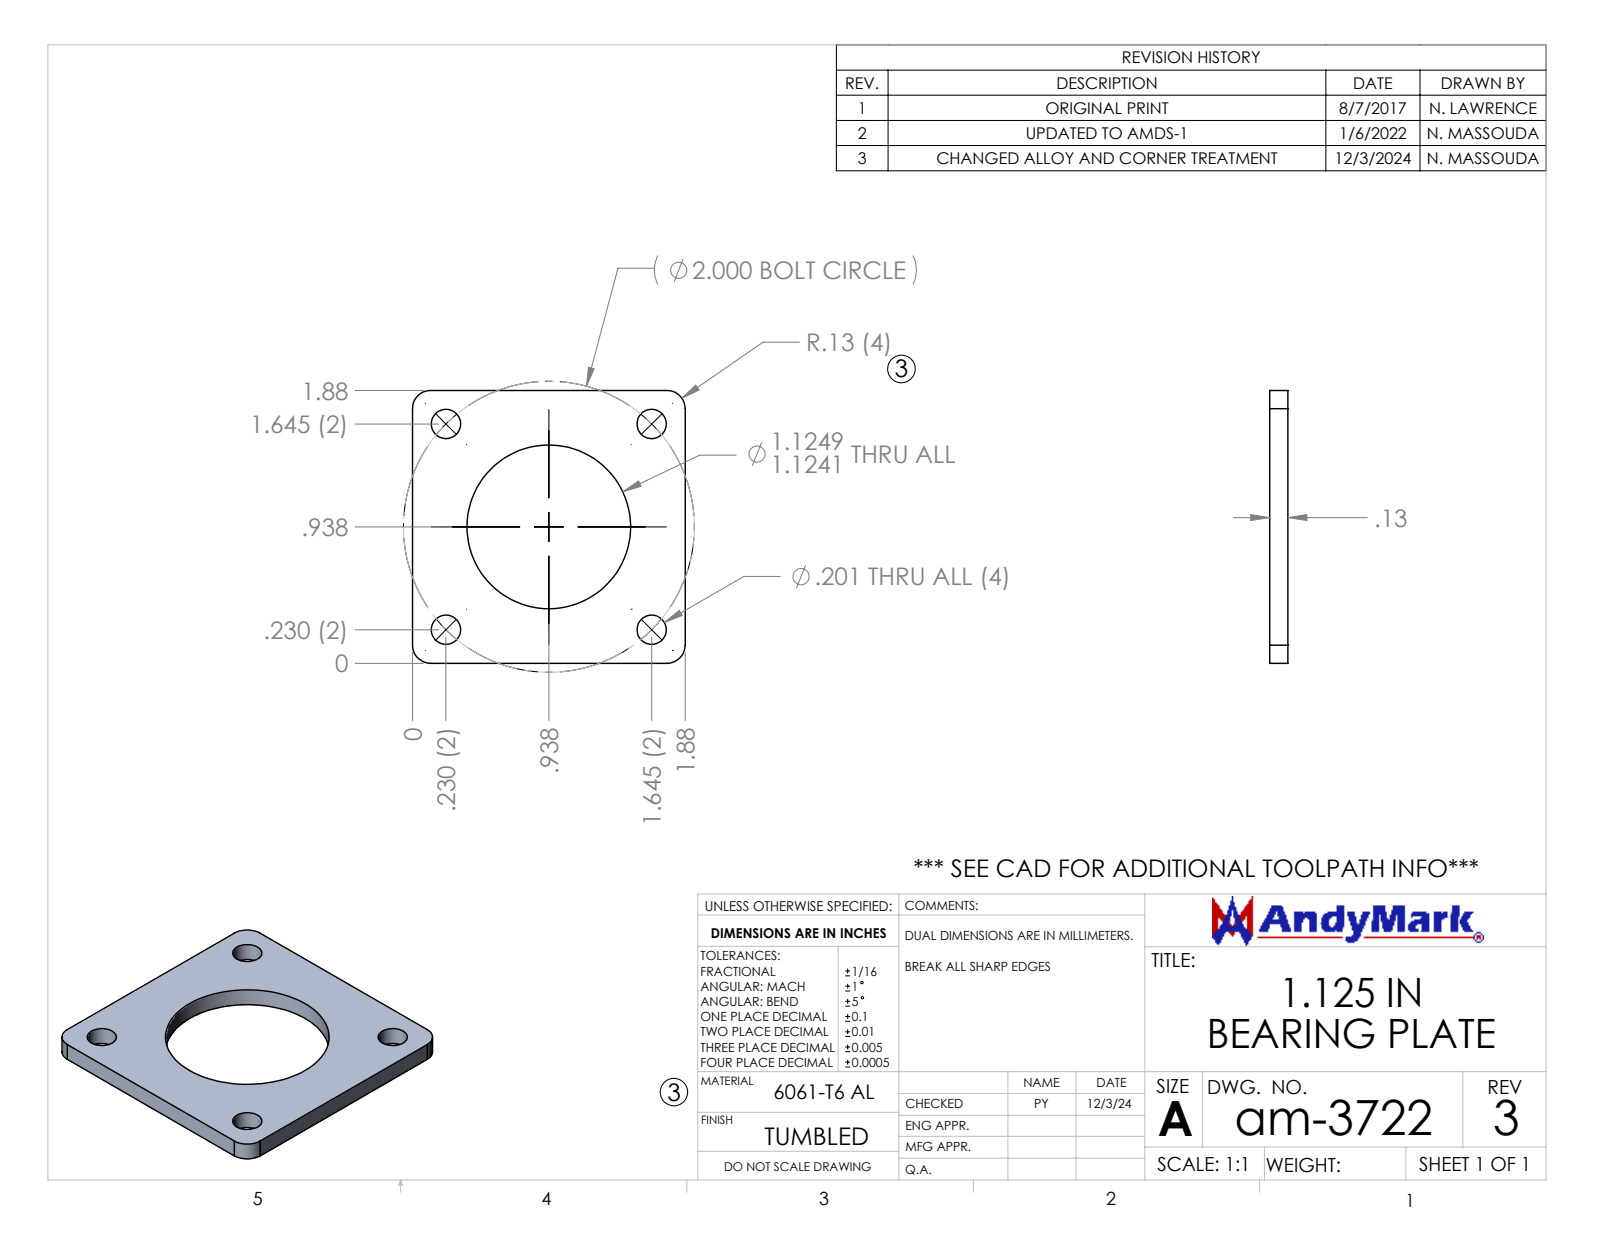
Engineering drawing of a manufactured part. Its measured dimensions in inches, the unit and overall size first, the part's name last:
Units: inches
Overall size (bounding box): 1.875 × 1.875 × 0.125
Round holes (diameter × count): ⌀0.201 ×4, ⌀1.125 ×1
Partial cylindrical surfaces — rounded edges, fillets, slot ends (radius × count): R0.125 ×4
Main face-to-face distances: 0.125, 1.875
Hole centre spacings: 1, 1.414, 2
Volume: 0.298 in³ · Surface area: 6.431 in²
Bodies: 1 solid, 20 faces (6 planar, 14 cylindrical, 0 other)
Part name (STEP PRODUCT): am-3722 1.125 Bearing Plate
STEP written by: SolidWorks 2024 (CONFIG_CONTROL_DESIGN)
